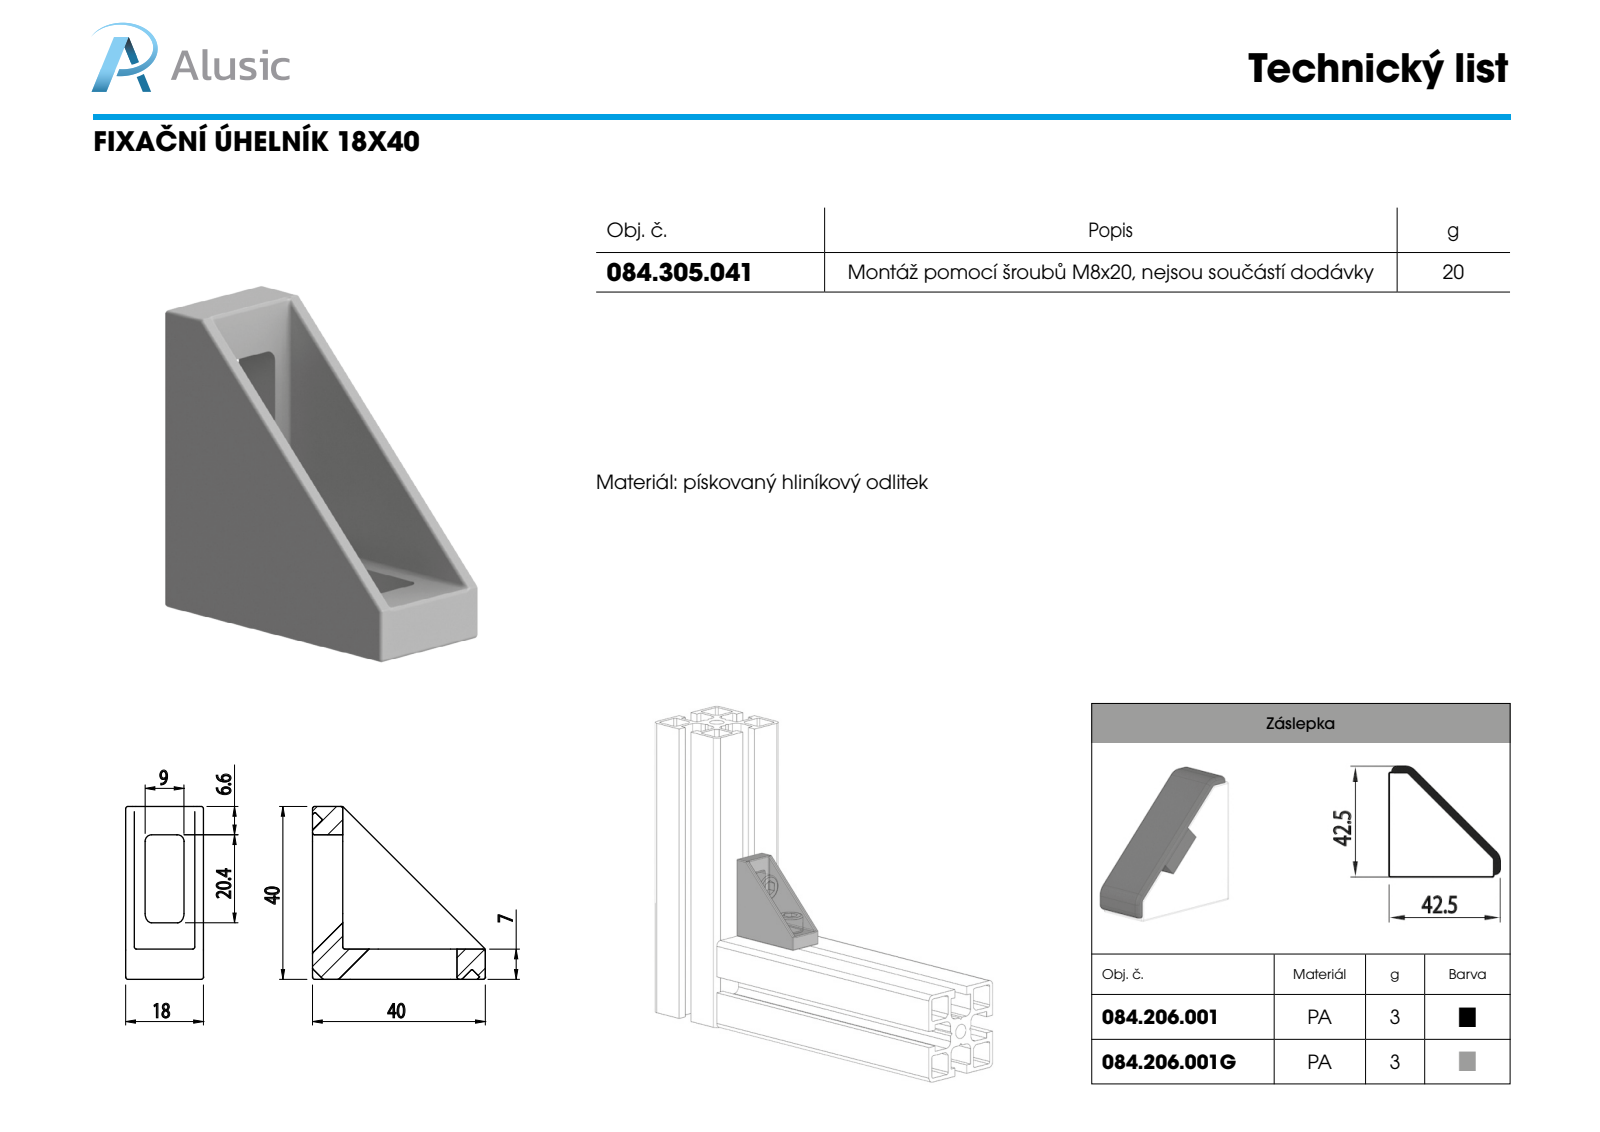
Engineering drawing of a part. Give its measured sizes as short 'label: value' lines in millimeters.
name: 084.305.041
written by: SolidWorks 2016 (CONFIG_CONTROL_DESIGN)
unit: mm
bodies: 1 solid, 144 faces (33 planar, 69 cylindrical, 42 other)
size: 40 × 40 × 18
volume: 8 244 mm³; area: 5 984 mm²
rounds: 32× R0.5, 23× R0.2, 8× R1.5
face distances: 18, 2, 16, 2.5, 4.5, 13.5, 11.5, 14, 7, 9
